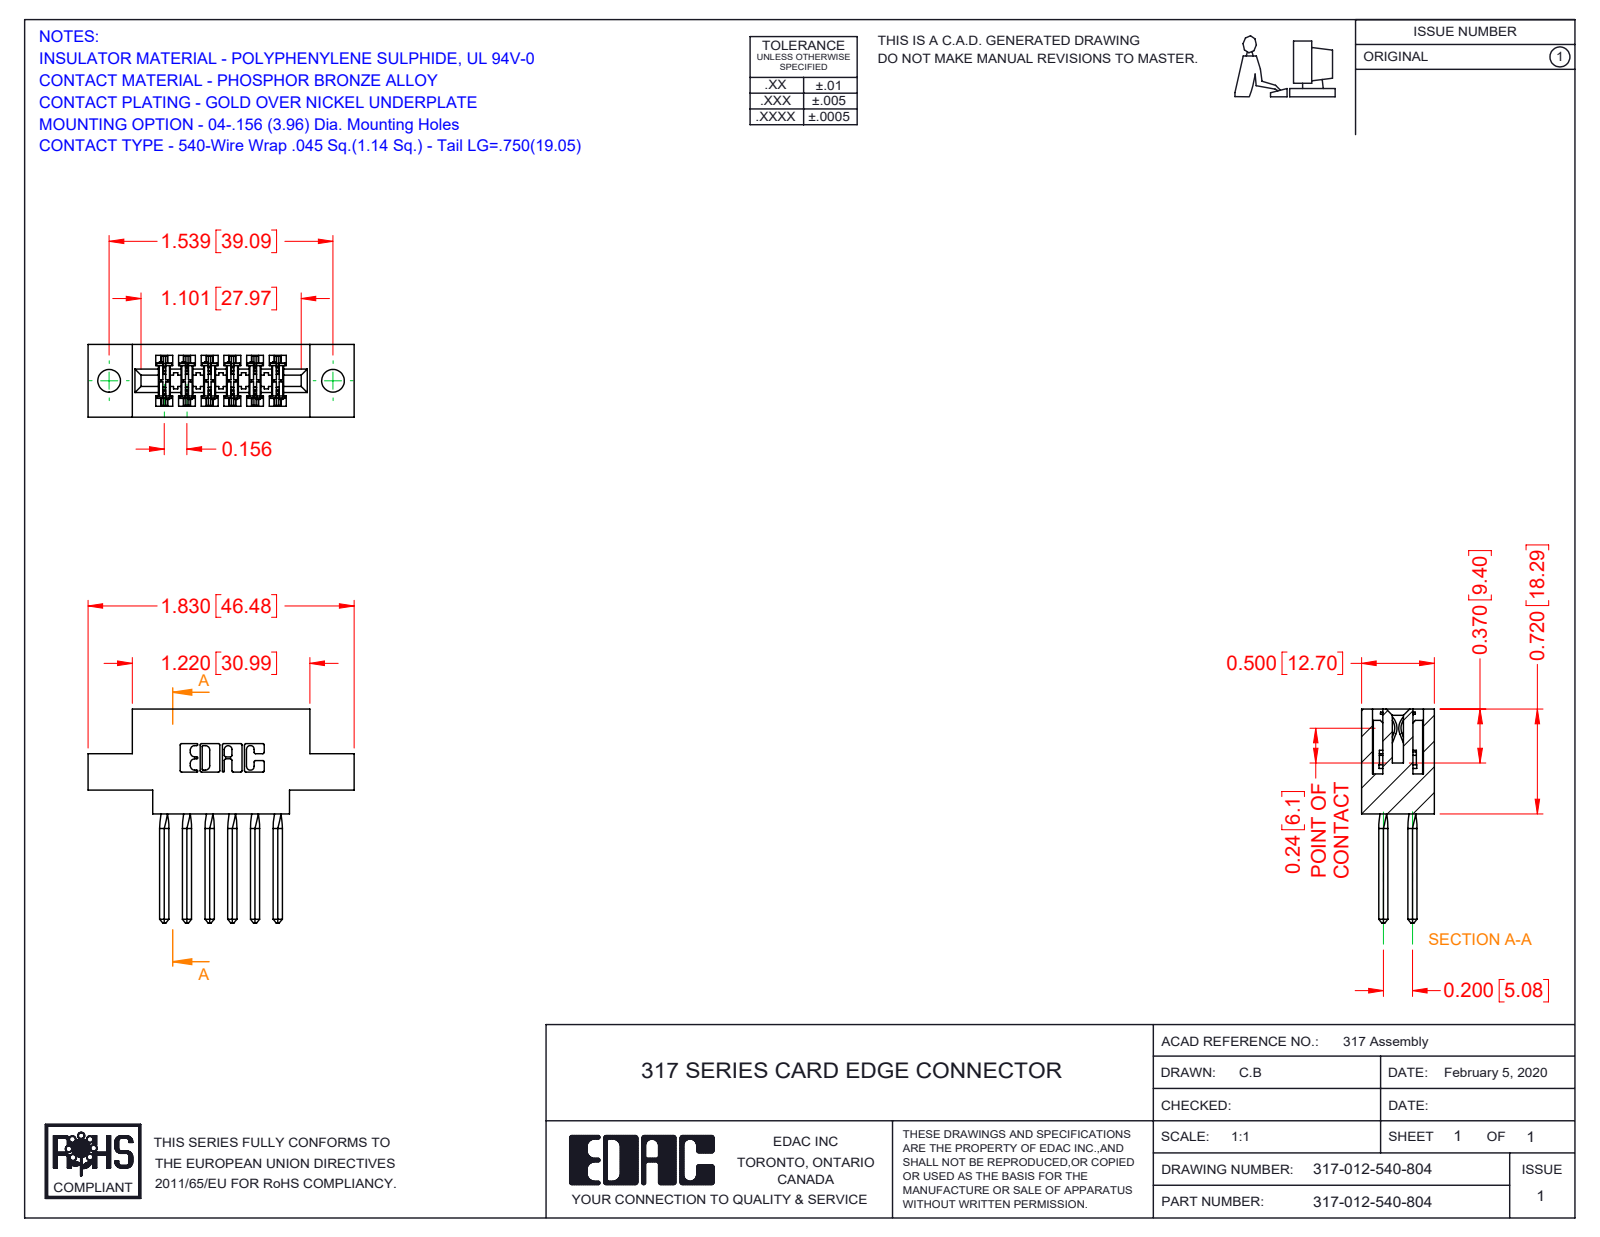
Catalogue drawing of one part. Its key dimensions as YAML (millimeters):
part_name: "317-290-001_540; 317-012-540-804; 317 Part_.156 Dia - TH"
step_written_by: "SolidWorks 2016 (CONFIG_CONTROL_DESIGN)"
units: millimeters
bodies: {solids: 13, faces: 1170, planar: 934, cylindrical: 188, other: 48}
overall_size: [46.5, 37.3, 12.7]
volume: 6490
surface_area: 8148
round_holes:
  - {diameter: 4, count: 2}
partial_cylinders:
  - {radius: 0.4, count: 24}
  - {radius: 0.3, count: 22}
  - {radius: 0.2, count: 6}
  - {radius: 0.8, count: 6}
  - {radius: 0.7, count: 3}
  - {radius: 2.4, count: 2}
  - {radius: 2.5, count: 2}
  - {radius: 2.8, count: 2}
face_to_face_distances: [12.7, 2.8, 1.9, 10.8, 5.6, 1.7, 4, 2.9, 4.1, 8.4]
hole_center_spacings: [39.1]
